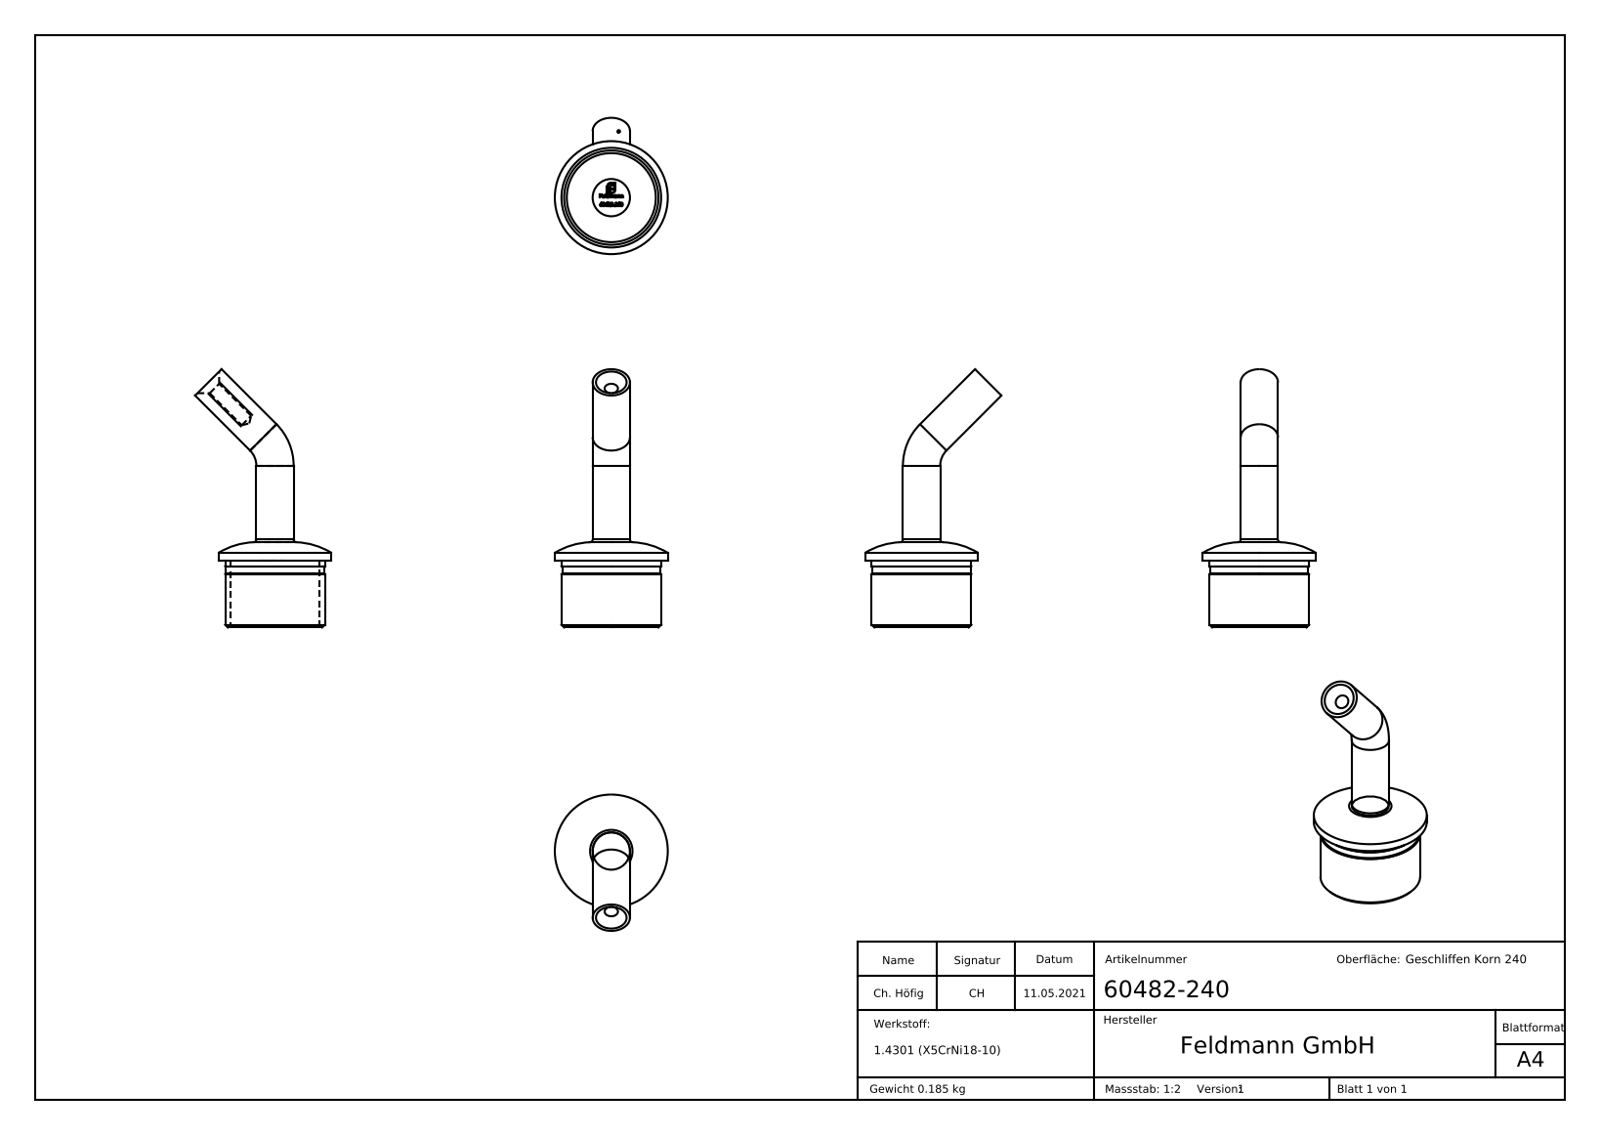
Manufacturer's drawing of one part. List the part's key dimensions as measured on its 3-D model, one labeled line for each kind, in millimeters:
Part name (STEP PRODUCT): 60482-240
STEP written by: SolidWorks 2018 (CONFIG_CONTROL_DESIGN)
Units: millimetres
Bodies: 1 solid, 311 faces (155 planar, 16 cylindrical, 140 other)
Overall size (bounding box): 96.95 × 51.17 × 42.4
Volume: 23 462 mm³ · Surface area: 12 194 mm²
Round holes (diameter × count): ⌀5 ×1, ⌀33.4 ×1
Round bosses / shafts (diameter × count): ⌀14 ×2, ⌀42.4 ×1, ⌀37.4 ×1, ⌀36.8 ×1
Main face-to-face distances: 25, 25.1, 3, 2.1, 23, 2, 20, 5, 5.1, 0.31
